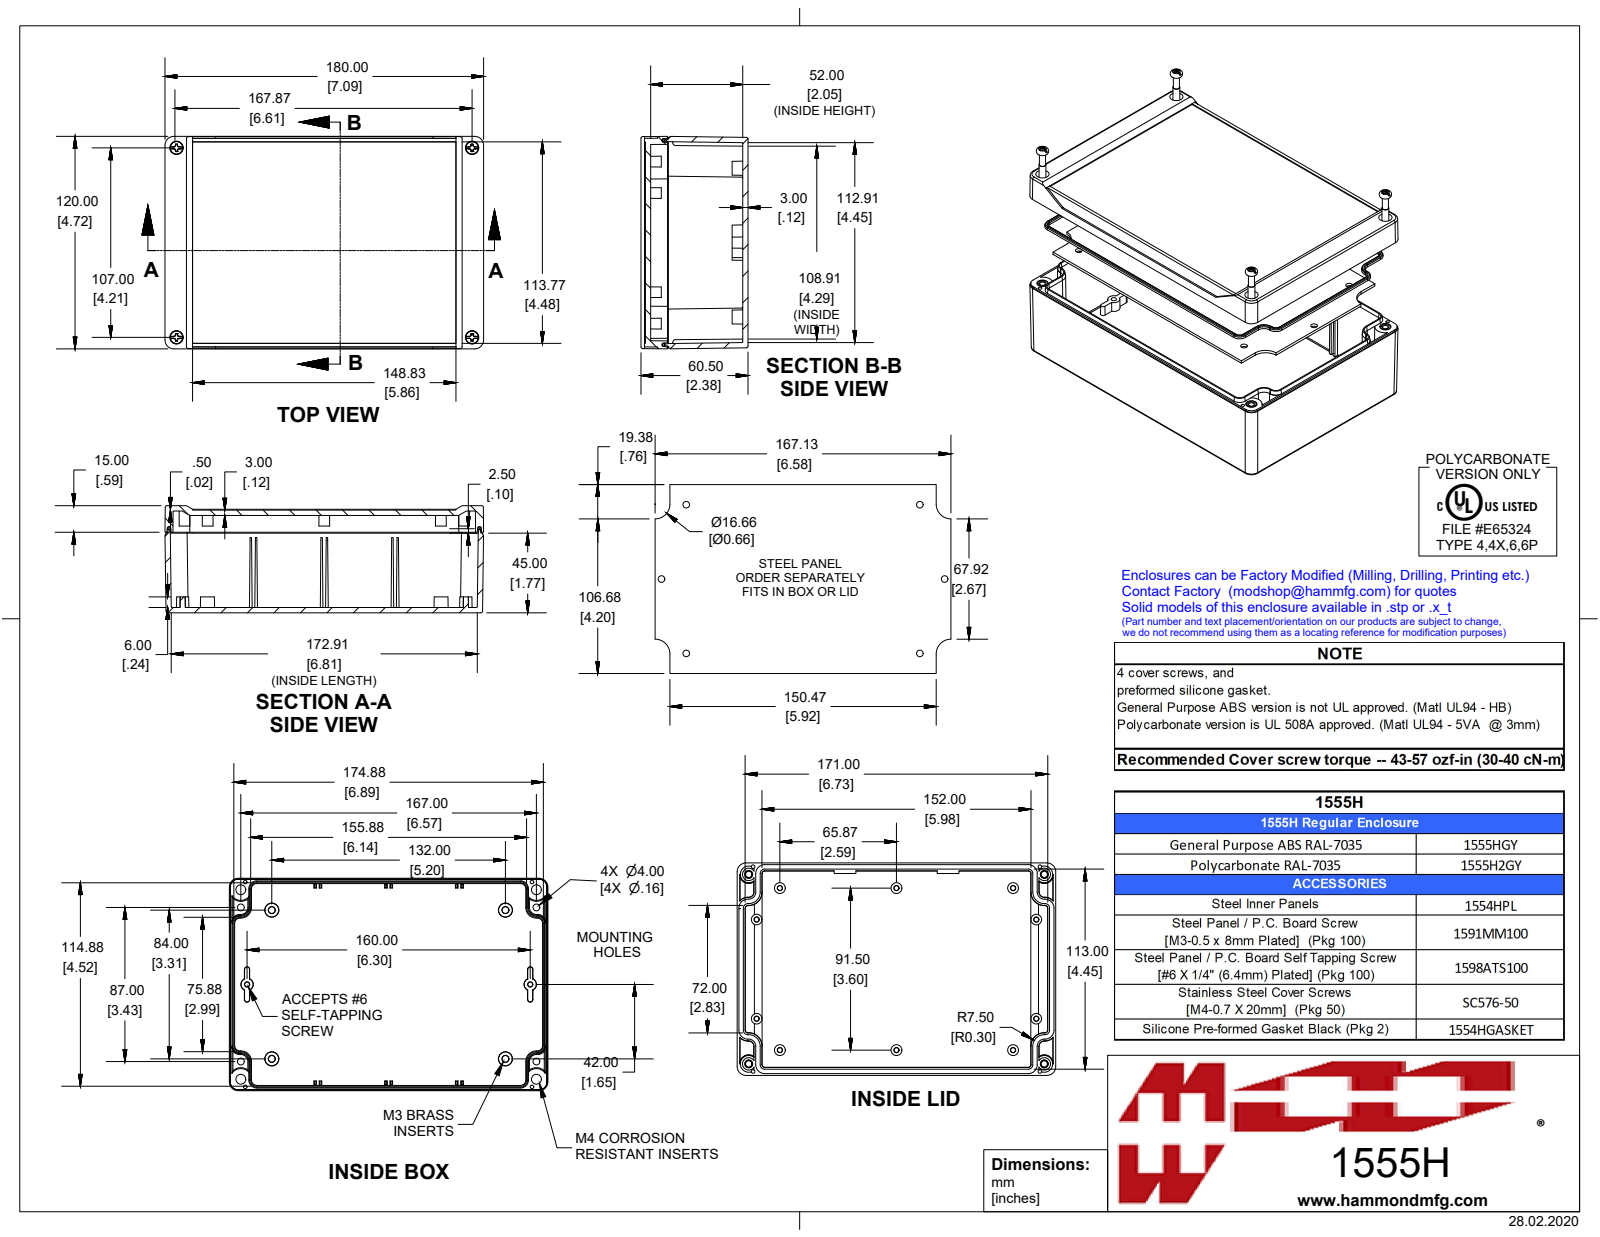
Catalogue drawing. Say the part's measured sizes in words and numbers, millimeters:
The part is named "1555H2GY". Its 3-D file was written by "SolidWorks 2019 (AUTOMOTIVE_DESIGN)". It is 16 solids with 1410 faces: 430 planar, 346 cylindrical and 634 other. Overall it measures 180 by 120 by 60.5 millimeters. Its volume is 274 500 cubic millimeters and its surface area 215 900 square millimeters. Round holes: 4 of diameter 2, 4 of diameter 2.5, 4 of diameter 3.3, 4 of diameter 3.5, 4 of diameter 3.7, 4 of diameter 7, 2 of diameter 2.8. Round bosses or shafts: 4 of diameter 6.4, 4 of diameter 6, 4 of diameter 5.5, 4 of diameter 5.3, 4 of diameter 4.8, 4 of diameter 3.9, 4 of diameter 3.9, 4 of diameter 3.8. Partial cylindrical surfaces (rounded edges, fillets, slot ends): 32 of radius 0.5, 8 of radius 1, 8 of radius 5, 4 of radius 4.7, 4 of radius 8.3, 2 of radius 1.5. The main face-to-face distances are 3, 55, 9, 6, 10.6, 7.6, 1.6, 49, 58, 47.4. The hole center spacings are 5, 20.9, 21.8, 44.3, 53.6, 57.8, 97.1, 100.9.
